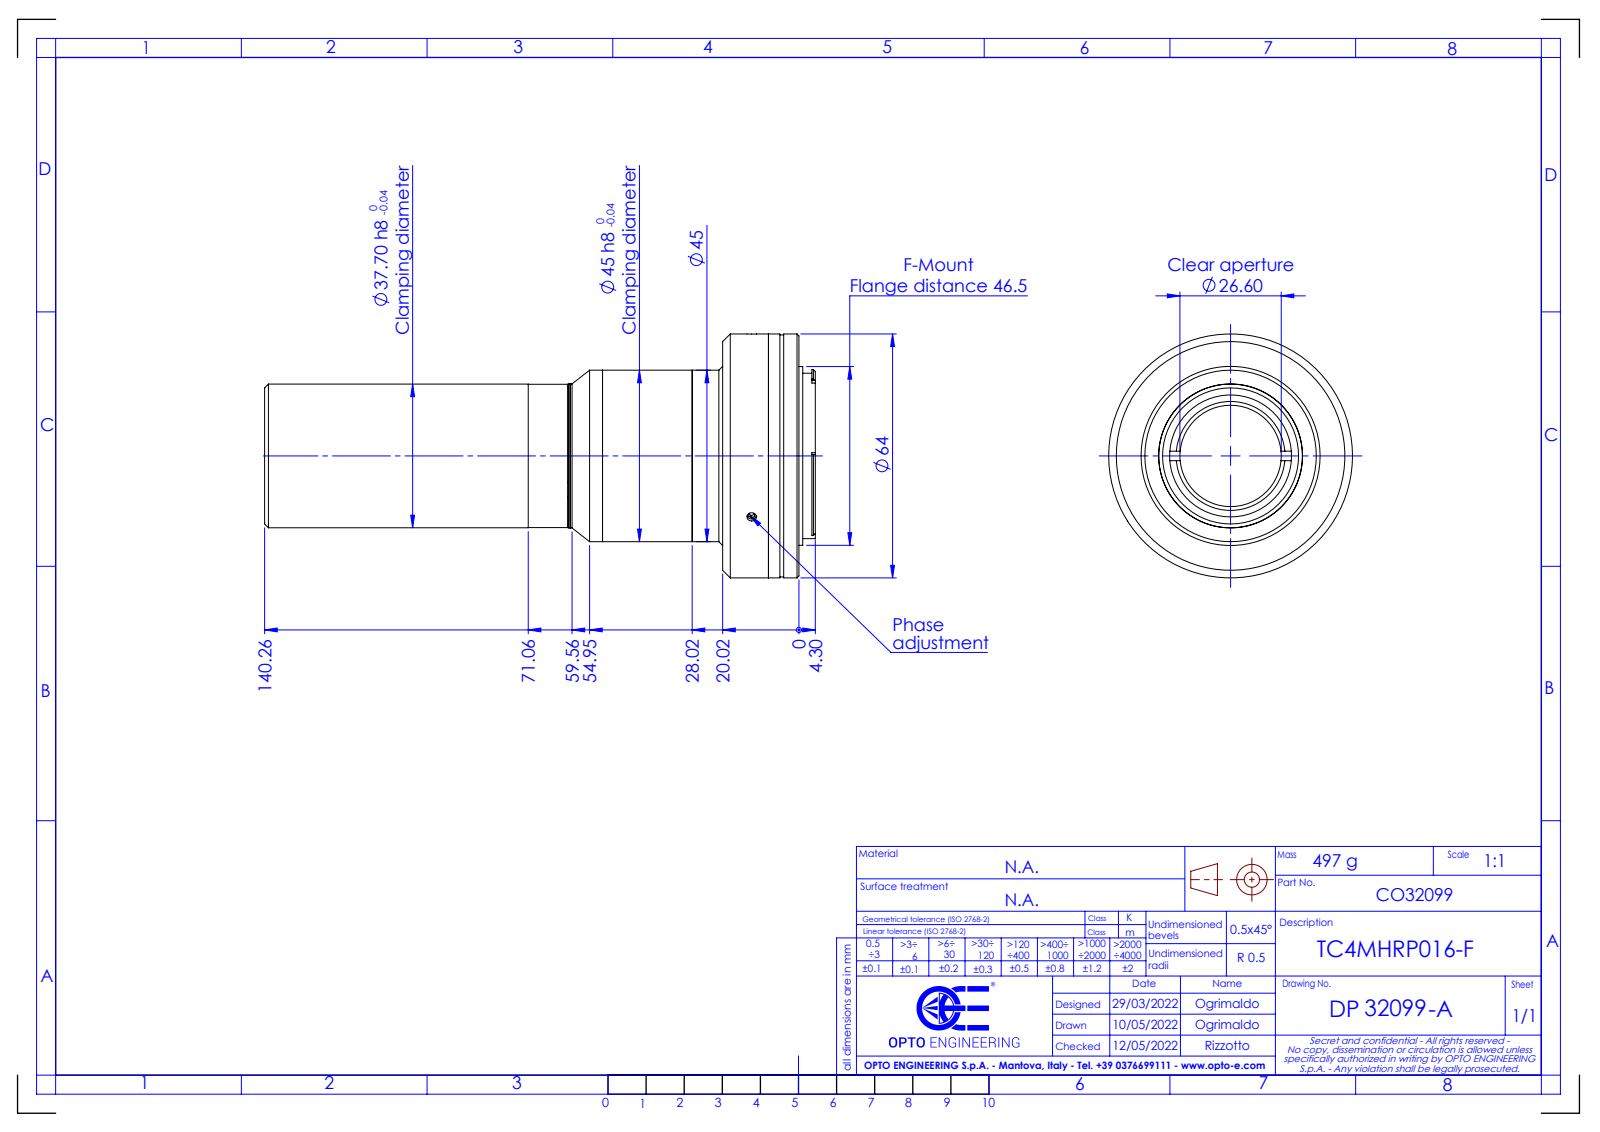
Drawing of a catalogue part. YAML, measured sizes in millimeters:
part_name: "DP32099-A_TC4MHRP016-F"
step_written_by: "SolidWorks 2021 (CONFIG_CONTROL_DESIGN)"
units: millimeters
bodies: {solids: 0, faces: 142, planar: 57, cylindrical: 57, other: 28}
overall_size: [144.56, 64, 64]
round_holes:
  - {diameter: 2.5, count: 3}
  - {diameter: 26.6, count: 1}
  - {diameter: 29, count: 1}
  - {diameter: 32, count: 1}
  - {diameter: 42, count: 1}
round_bosses_or_shafts:
  - {diameter: 64, count: 1}
  - {diameter: 63.5, count: 1}
  - {diameter: 46.9, count: 1}
  - {diameter: 45, count: 1}
  - {diameter: 43.4, count: 1}
  - {diameter: 37.8, count: 1}
  - {diameter: 37.7, count: 1}
  - {diameter: 37.6, count: 1}
partial_cylinders:
  - {radius: 0.5, count: 6}
  - {radius: 1.15, count: 2}
  - {radius: 22.65, count: 1}
face_to_face_distances: [4.99, 15.02, 20.01, 16.01, 0.99, 4, 3.75, 3, 52.56, 9]
